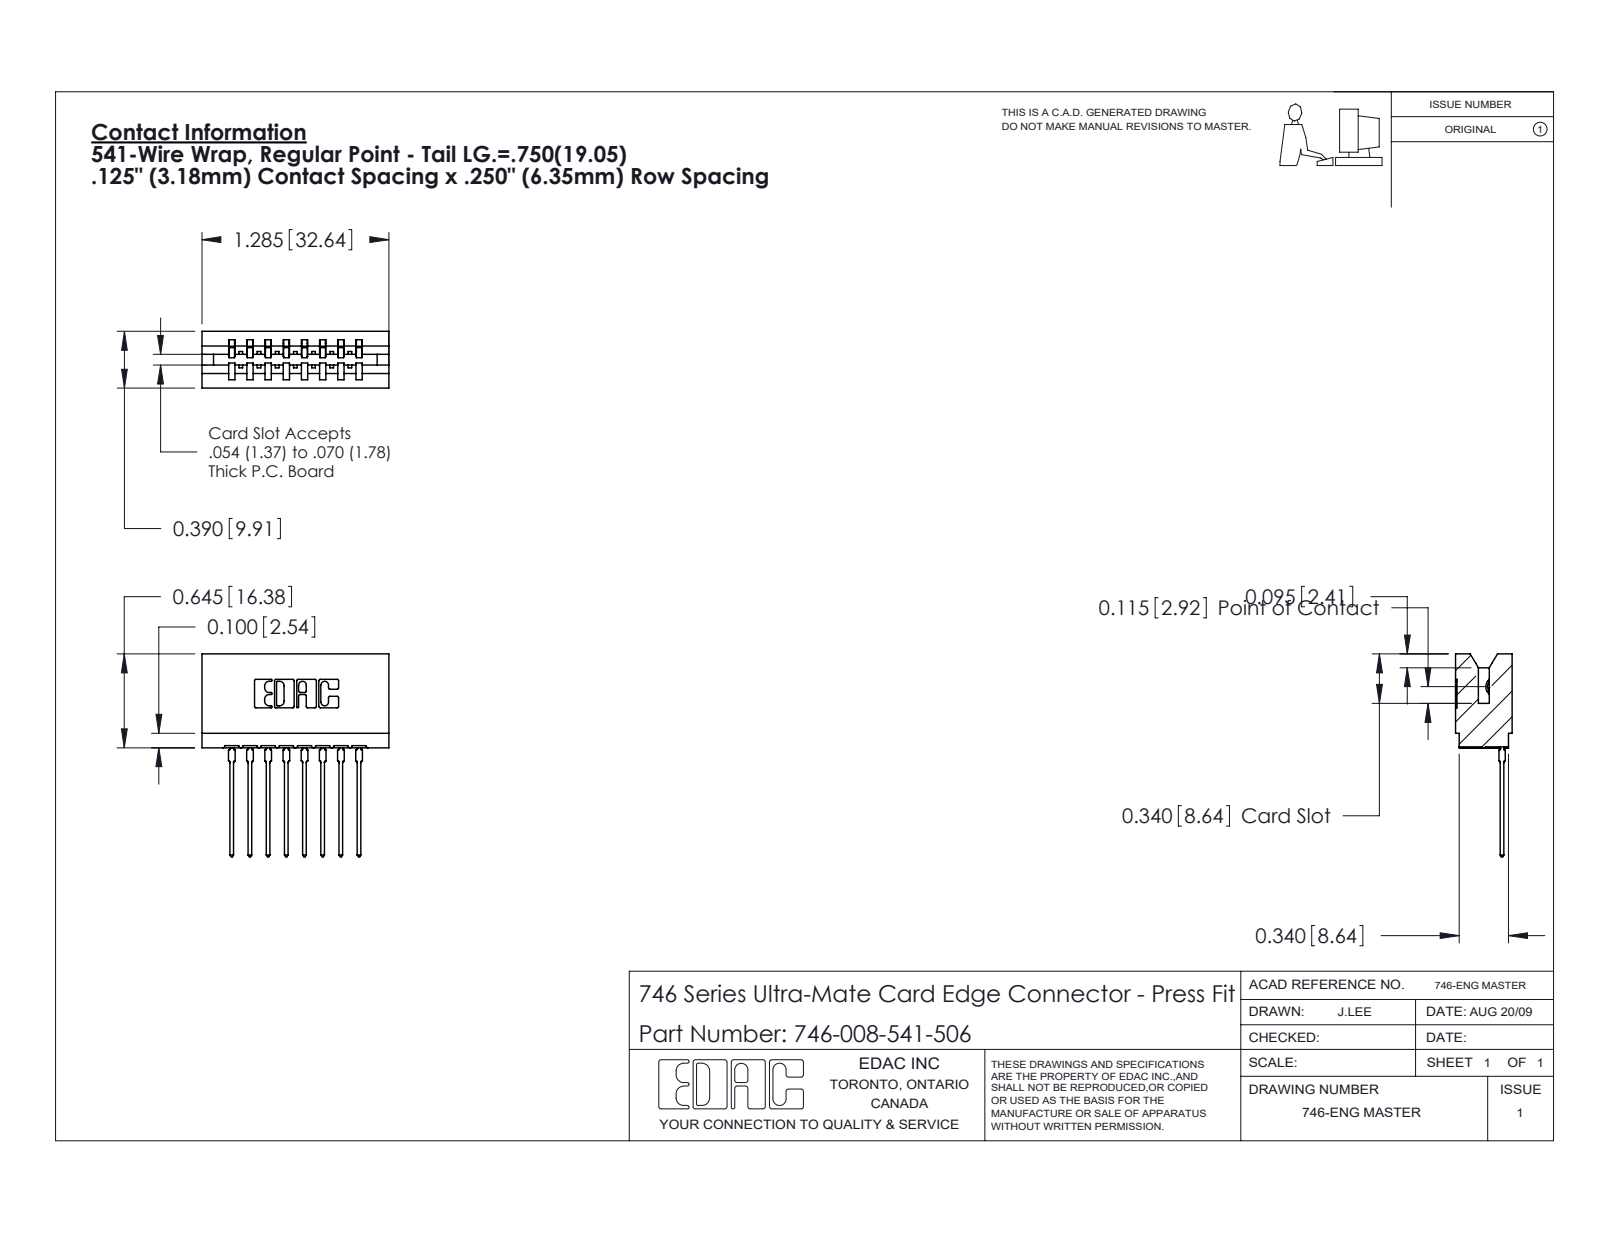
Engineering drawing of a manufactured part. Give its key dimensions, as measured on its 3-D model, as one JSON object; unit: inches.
{"part_name": "746-292-001_541; 746 Part_.340 Slot Depth - 06; 746-008-541-506", "step_written_by": "SolidWorks 2020 (CONFIG_CONTROL_DESIGN)", "units": "inches", "bodies": {"solids": 9, "faces": 962, "planar": 560, "cylindrical": 194, "other": 208}, "overall_size": [1.394, 1.285, 0.39], "volume_in3": 0.237, "surface_area_in2": 7.645, "partial_cylinders_radius": [[0.01, 22], [0.021, 16], [0.015, 9], [0.007, 6], [0.031, 6], [0.005, 4], [0.011, 4], [0.026, 3]], "face_to_face_distances": [0.25, 0.042, 0.125, 0.5, 0.333, 0.057, 0.292, 0.375, 0.208, 0.125]}
